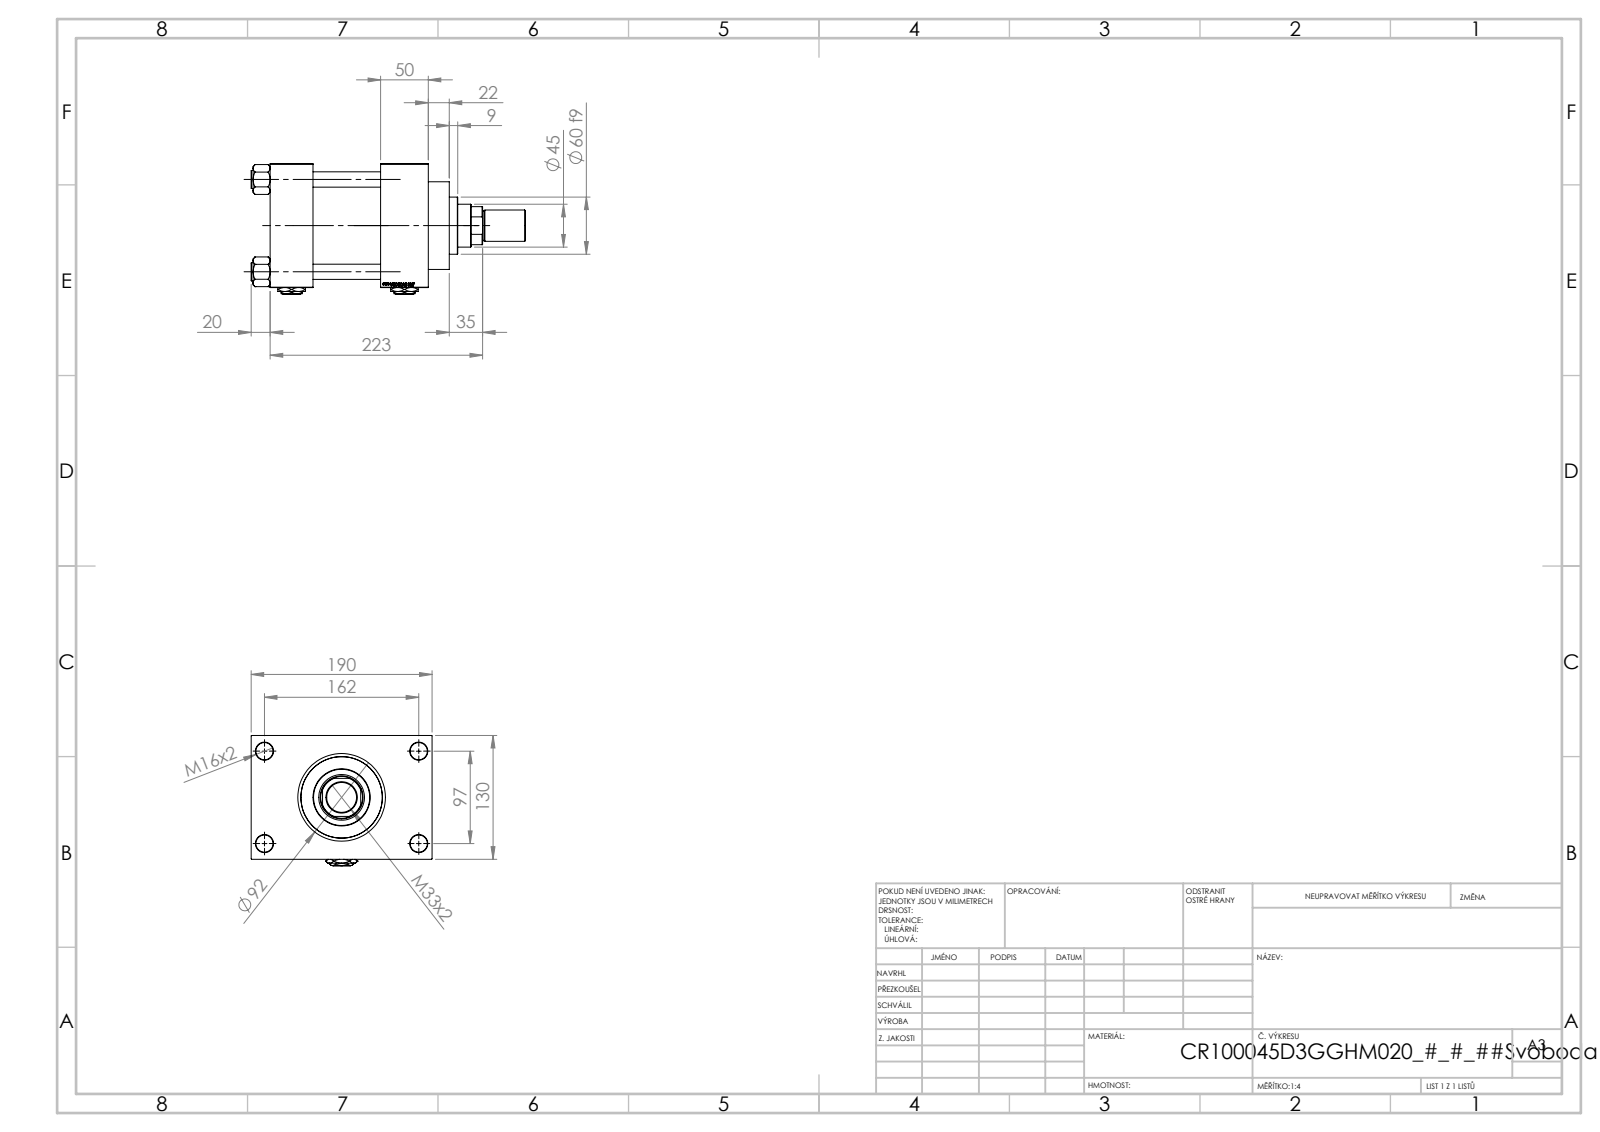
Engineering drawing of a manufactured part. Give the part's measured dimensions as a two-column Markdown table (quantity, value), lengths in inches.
| quantity | value |
| --- | --- |
| part name | Zatka_pro_OIL_PORT; V215CR_D_TYCINKA; NUT_M5_D; ROD_END_AH (+3 more) |
| STEP written by | SolidWorks 2019 (CONFIG_CONTROL_DESIGN) |
| units | inches |
| bodies | 14 solids, 1267 faces (597 planar, 104 cylindrical, 566 other) |
| overall size | 11.339 × 7.48 × 5.394 |
| volume | 160.6 in³ |
| surface area | 567 in² |
| round holes (diameter × count) | 0.63 × 4, 0.709 × 4, 0.276 × 2, 1.041 × 2, 1.378 × 2, 1.24 × 1, 1.772 × 1, 1.89 × 1, 2.992 × 1, 3.366 × 1, 3.937 × 1 |
| round bosses / shafts (diameter × count) | 0.748 × 4, 4.173 × 1, 3.622 × 1, 2.362 × 1, 1.299 × 1, 1.22 × 1 |
| partial cylindrical surfaces (radius × count) | 0.866 × 1 |
| main face-to-face distances | 1.772, 5.118, 4.567, 2.795, 6.535, 4.764, 1.969, 6.299, 1.181, 0.787 |
| hole center spacings | 1.281, 2.698, 3.717, 3.815, 4.026, 5.096, 6.367, 3.819 |
